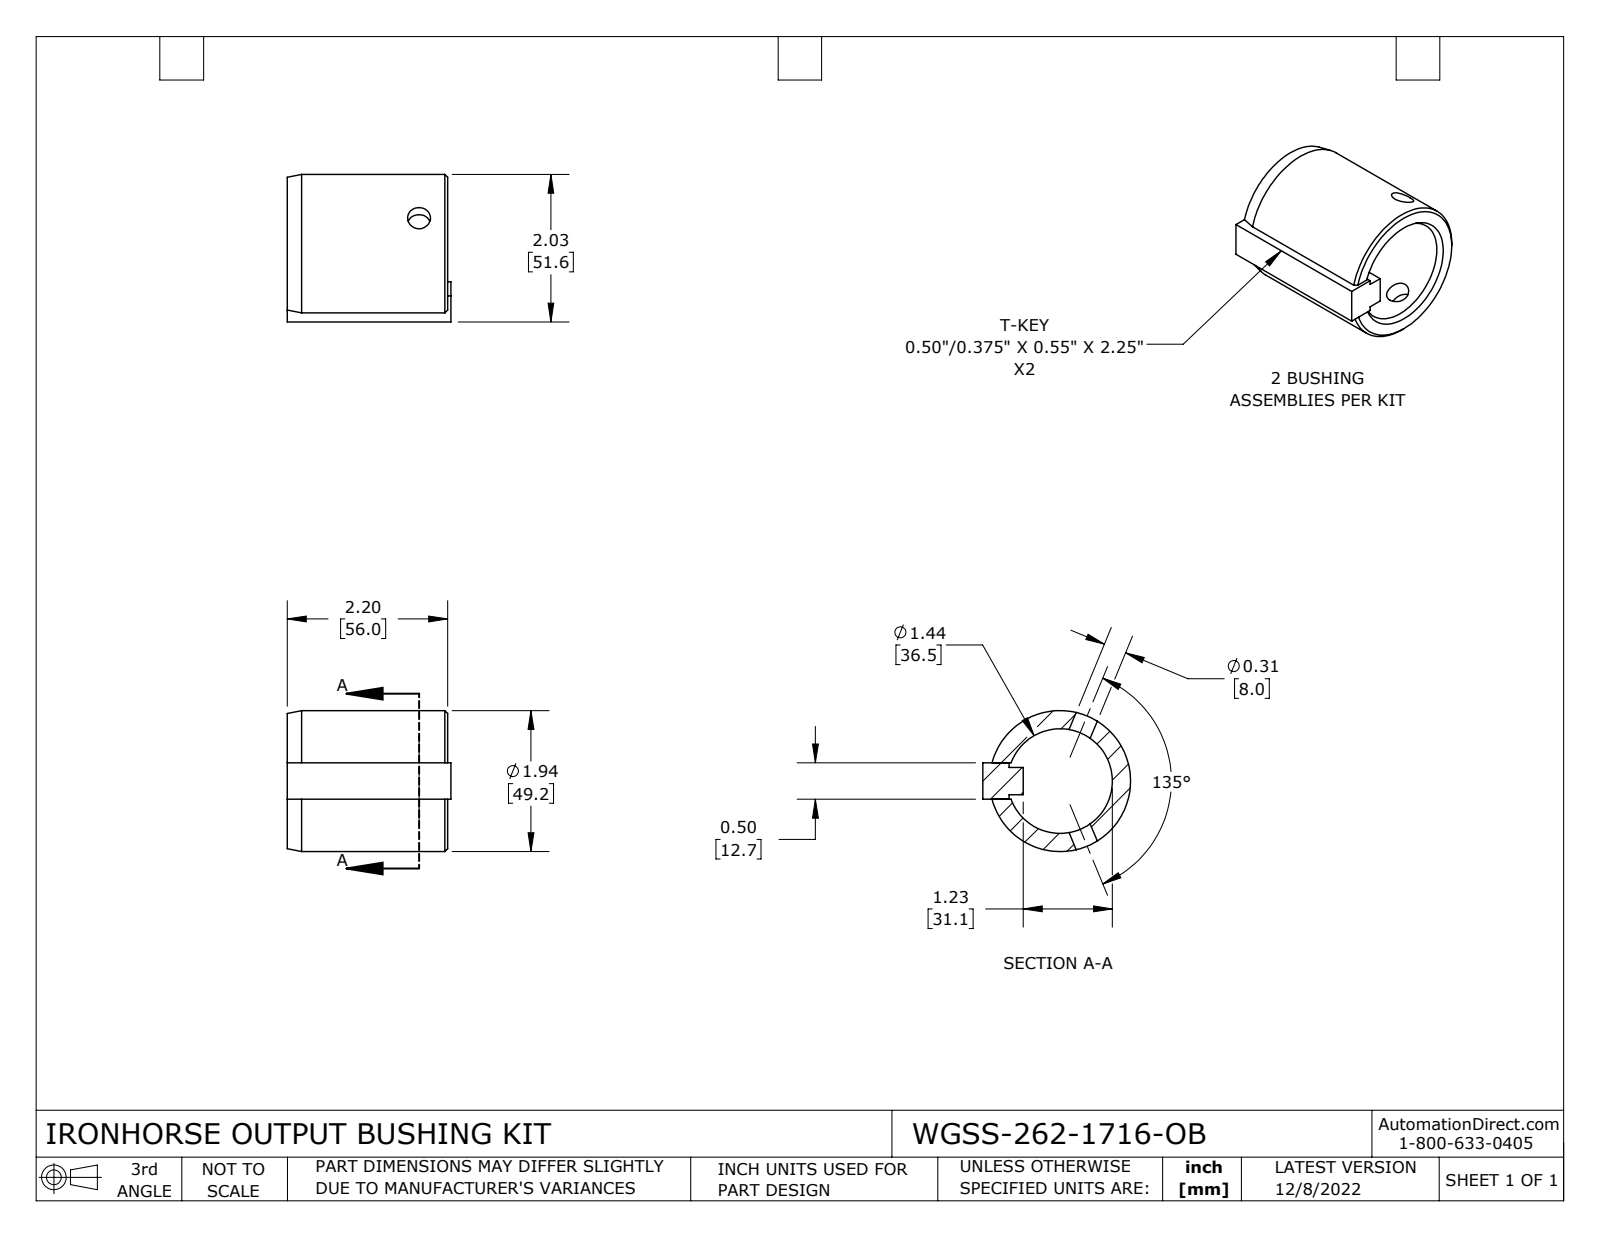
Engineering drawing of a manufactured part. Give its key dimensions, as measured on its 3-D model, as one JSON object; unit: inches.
{"part_name": "WGSS-262-1716-OB", "step_written_by": "SolidWorks 2021 (CONFIG_CONTROL_DESIGN)", "units": "inches", "bodies": {"solids": 2, "faces": 34, "planar": 14, "cylindrical": 10, "other": 10}, "overall_size": [2.25, 2.03, 1.937], "volume_in3": 3.132, "surface_area_in2": 29.51, "round_holes": [[0.315, 2], [1.437, 1]], "round_bosses_or_shafts": [[1.937, 1]], "face_to_face_distances": [0.5, 0.554, 2.205, 0.437, 0.063, 0.062, 0.375, 0.438, 0.195, 0.359]}
